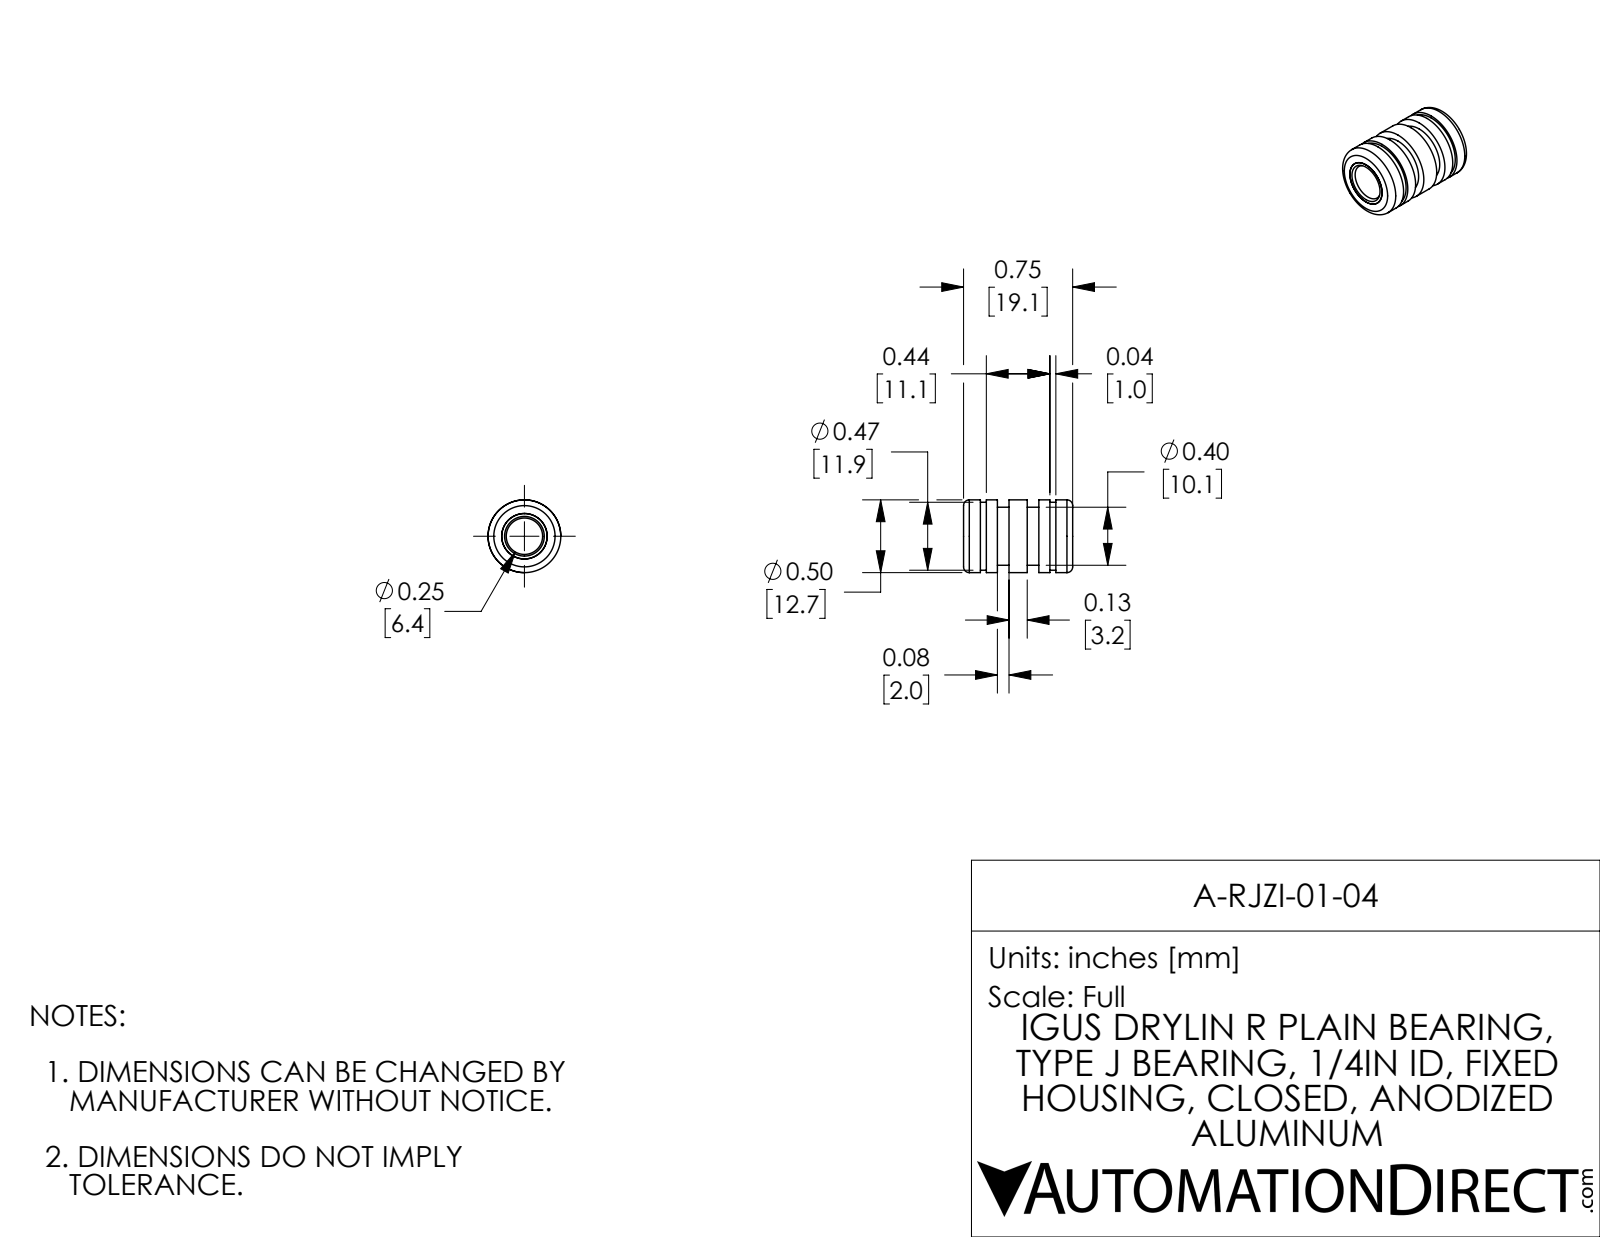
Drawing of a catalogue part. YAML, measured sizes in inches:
part_name: "A-RJZI-01-04"
step_written_by: "SolidWorks 2017 (AUTOMOTIVE_DESIGN)"
units: inches
bodies: {solids: 3, faces: 54, planar: 14, cylindrical: 28, other: 12}
overall_size: [0.75, 0.5, 0.5]
volume: 0.096
surface_area: 3.832
round_holes:
  - {diameter: 0.25, count: 1}
  - {diameter: 0.312, count: 1}
round_bosses_or_shafts:
  - {diameter: 0.5, count: 1}
  - {diameter: 0.467, count: 1}
  - {diameter: 0.399, count: 1}
  - {diameter: 0.313, count: 1}
face_to_face_distances: [0.233, 0.313, 0.438, 0.518, 0.205, 0.08, 0.75, 0.285, 0.125, 0.375]
